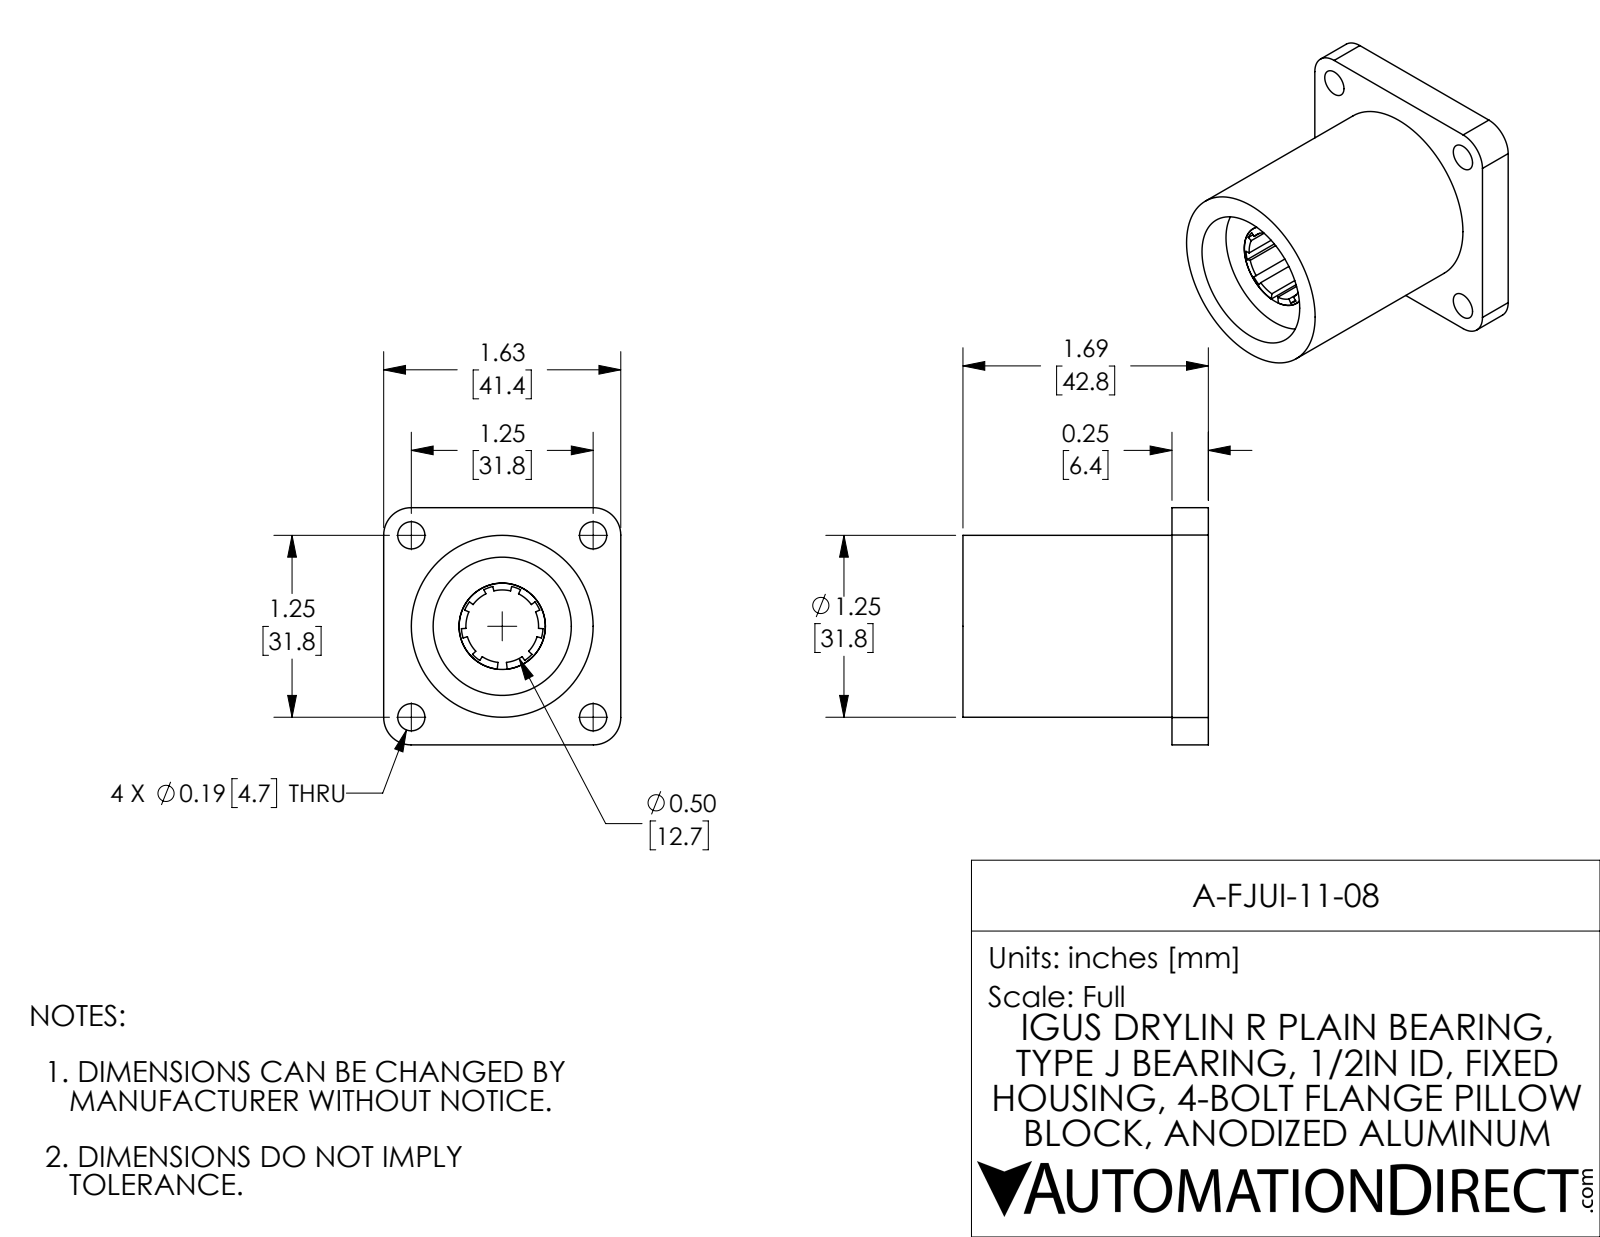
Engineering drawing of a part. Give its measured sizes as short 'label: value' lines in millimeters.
name: A-FJUI-11-08
written by: SolidWorks 2017 (AUTOMOTIVE_DESIGN)
unit: mm
bodies: 2 solids, 117 faces (64 planar, 53 cylindrical, 0 other)
size: 42.8 × 41.4 × 41.4
volume: 29 600 mm³; area: 13 590 mm²
holes: 4× ⌀4.7, 1× ⌀24.1
bosses: 1× ⌀31.8, 1× ⌀15.1, 1× ⌀2.6
rounds: 4× R4.8, 1× R6.4, 1× R7.1, 1× R8.3
face distances: 6.4, 41.4, 42.8, 36.5, 36.9, 30.6, 5.9, 5.9, 0.4, 31
hole spacings: 22.5, 31.8, 44.9
